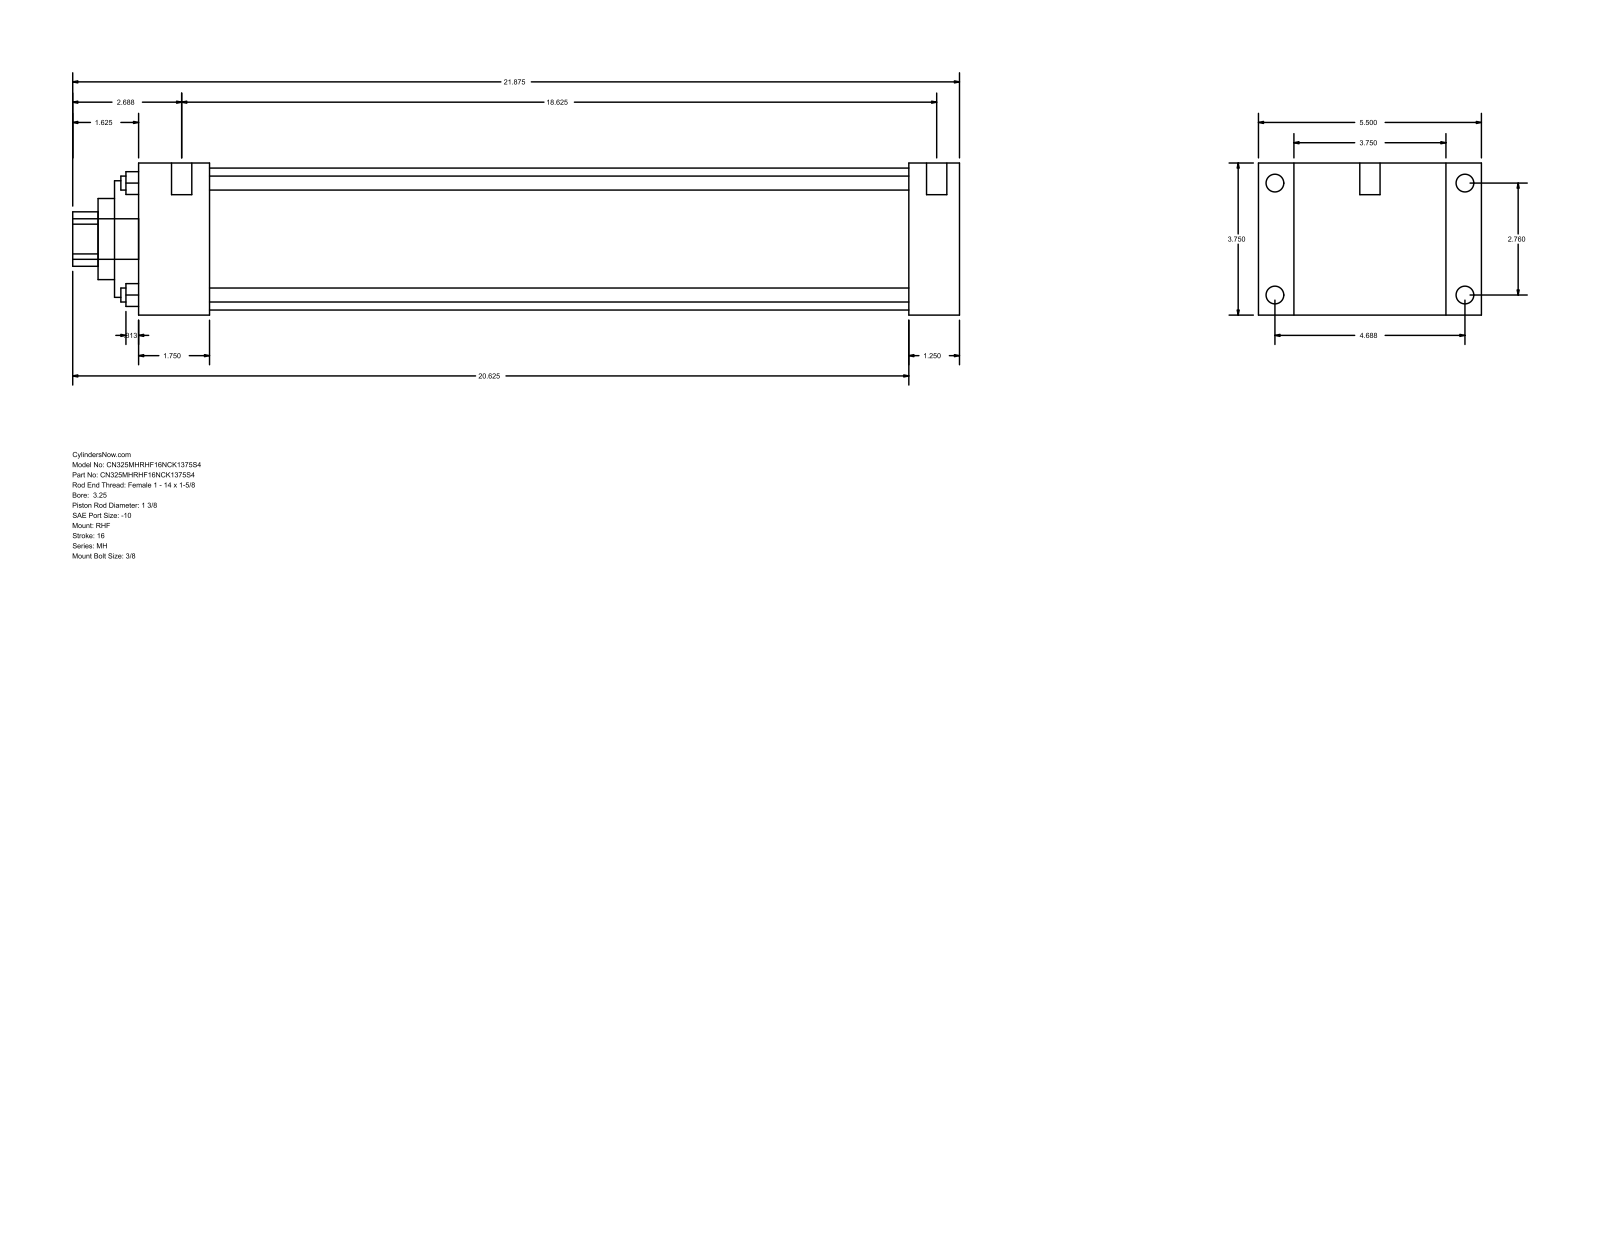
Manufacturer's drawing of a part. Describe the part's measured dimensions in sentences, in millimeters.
The part is named "MH_RHF__0325_1.375". Its 3-D file was written by "GSSL Pune (CONFIG_CONTROL_DESIGN)". It is 0 solids with 90 faces: 61 planar, 29 cylindrical and 0 other. Overall it measures 555.62 by 139.7 by 95.25 millimeters. Round holes: 4 of diameter 8.76, 1 of diameter 34.92, 1 of diameter 50.8, 1 of diameter 73.03, 1 of diameter 88.9. Round bosses or shafts: 4 of diameter 11.13, 4 of diameter 5.56, 2 of diameter 12.7, 1 of diameter 25.4. Partial cylindrical surfaces (rounded edges, fillets, slot ends): 1 of radius 17.06. The main face-to-face distances are 95.24, 31.74, 22.23, 117.47, 482.61, 514.35, 139.7, 44.45, 438.16, 469.9. The hole center spacings are 49.57, 70.1, 99.14.
